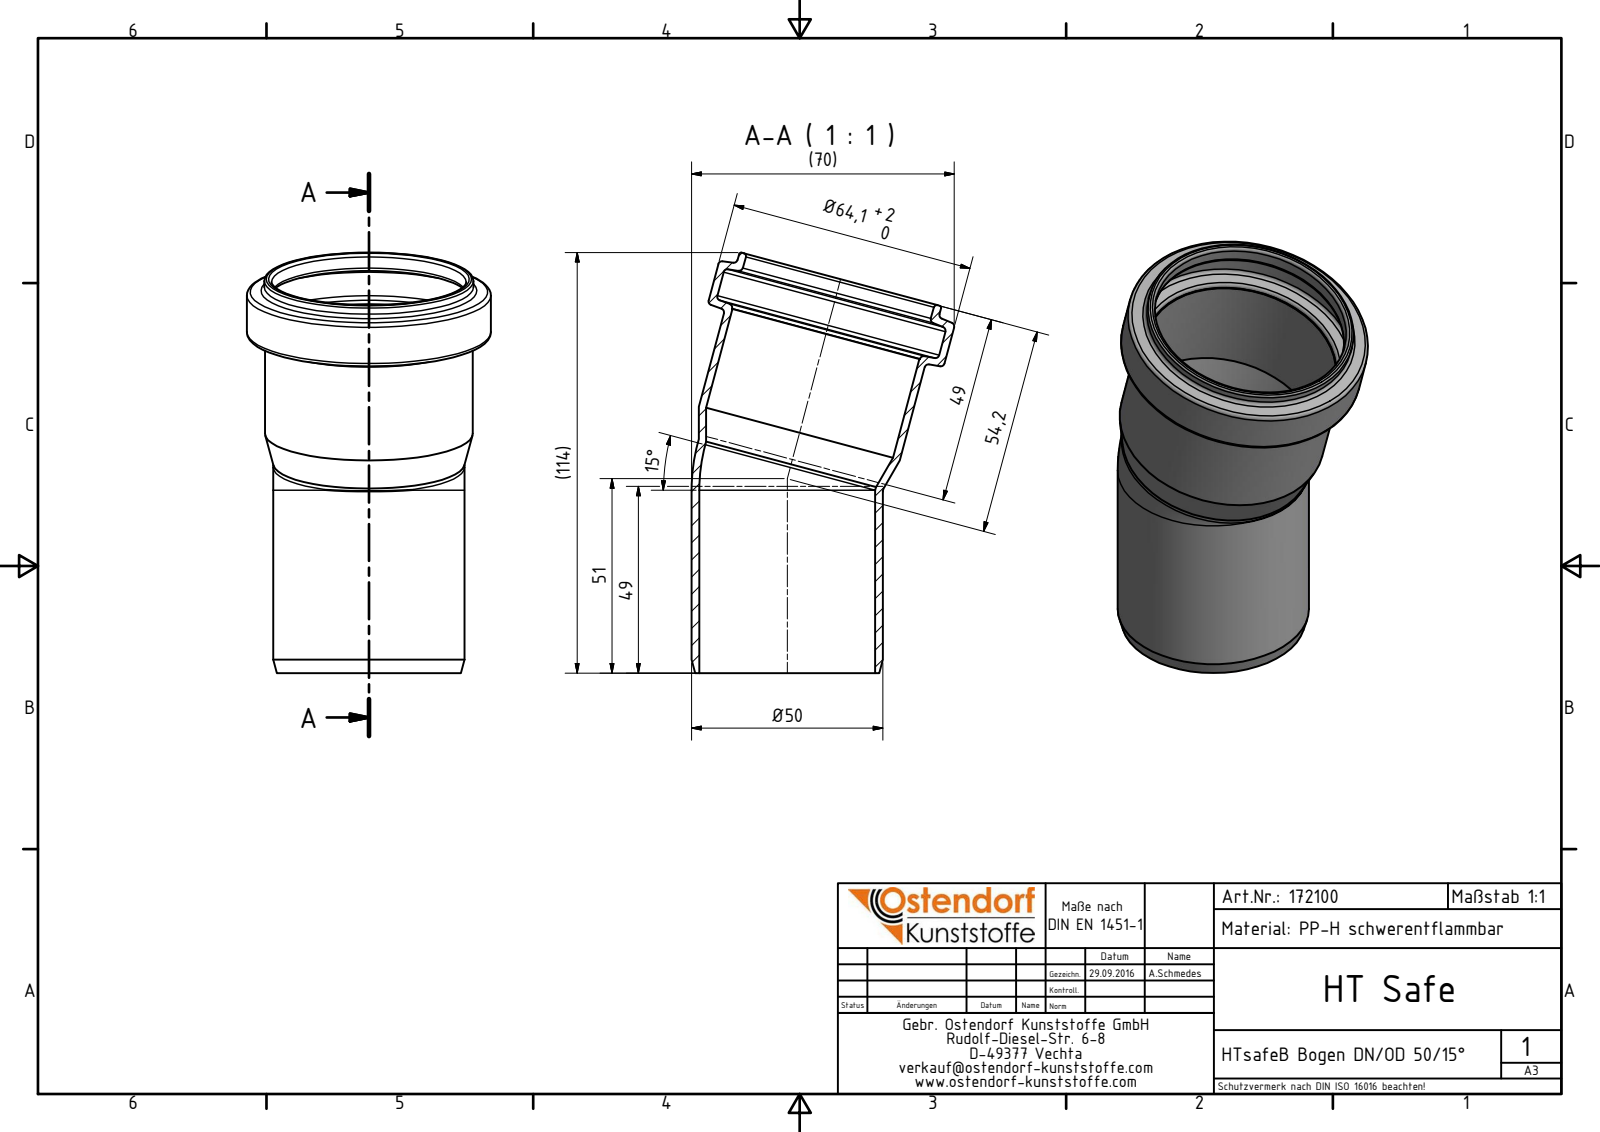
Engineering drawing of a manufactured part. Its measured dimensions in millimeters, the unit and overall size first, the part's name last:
Units: millimetres
Overall size (bounding box): 110.34 × 68.96 × 64.1
Round holes (diameter × count): ⌀46.2 ×2, ⌀50.8 ×1, ⌀51.1 ×1, ⌀60.3 ×1
Round bosses / shafts (diameter × count): ⌀50.2 ×2, ⌀64.1 ×1, ⌀54.9 ×1, ⌀54.6 ×1
Main face-to-face distances: 14.91
Volume: 35 439 mm³ · Surface area: 36 831 mm²
Bodies: 1 solid, 34 faces (3 planar, 11 cylindrical, 20 other)
Part name (STEP PRODUCT): 172100 HTsafeB DN_OD 50_15°
STEP written by: Autodesk Inventor 2016 (AUTOMOTIVE_DESIGN)
